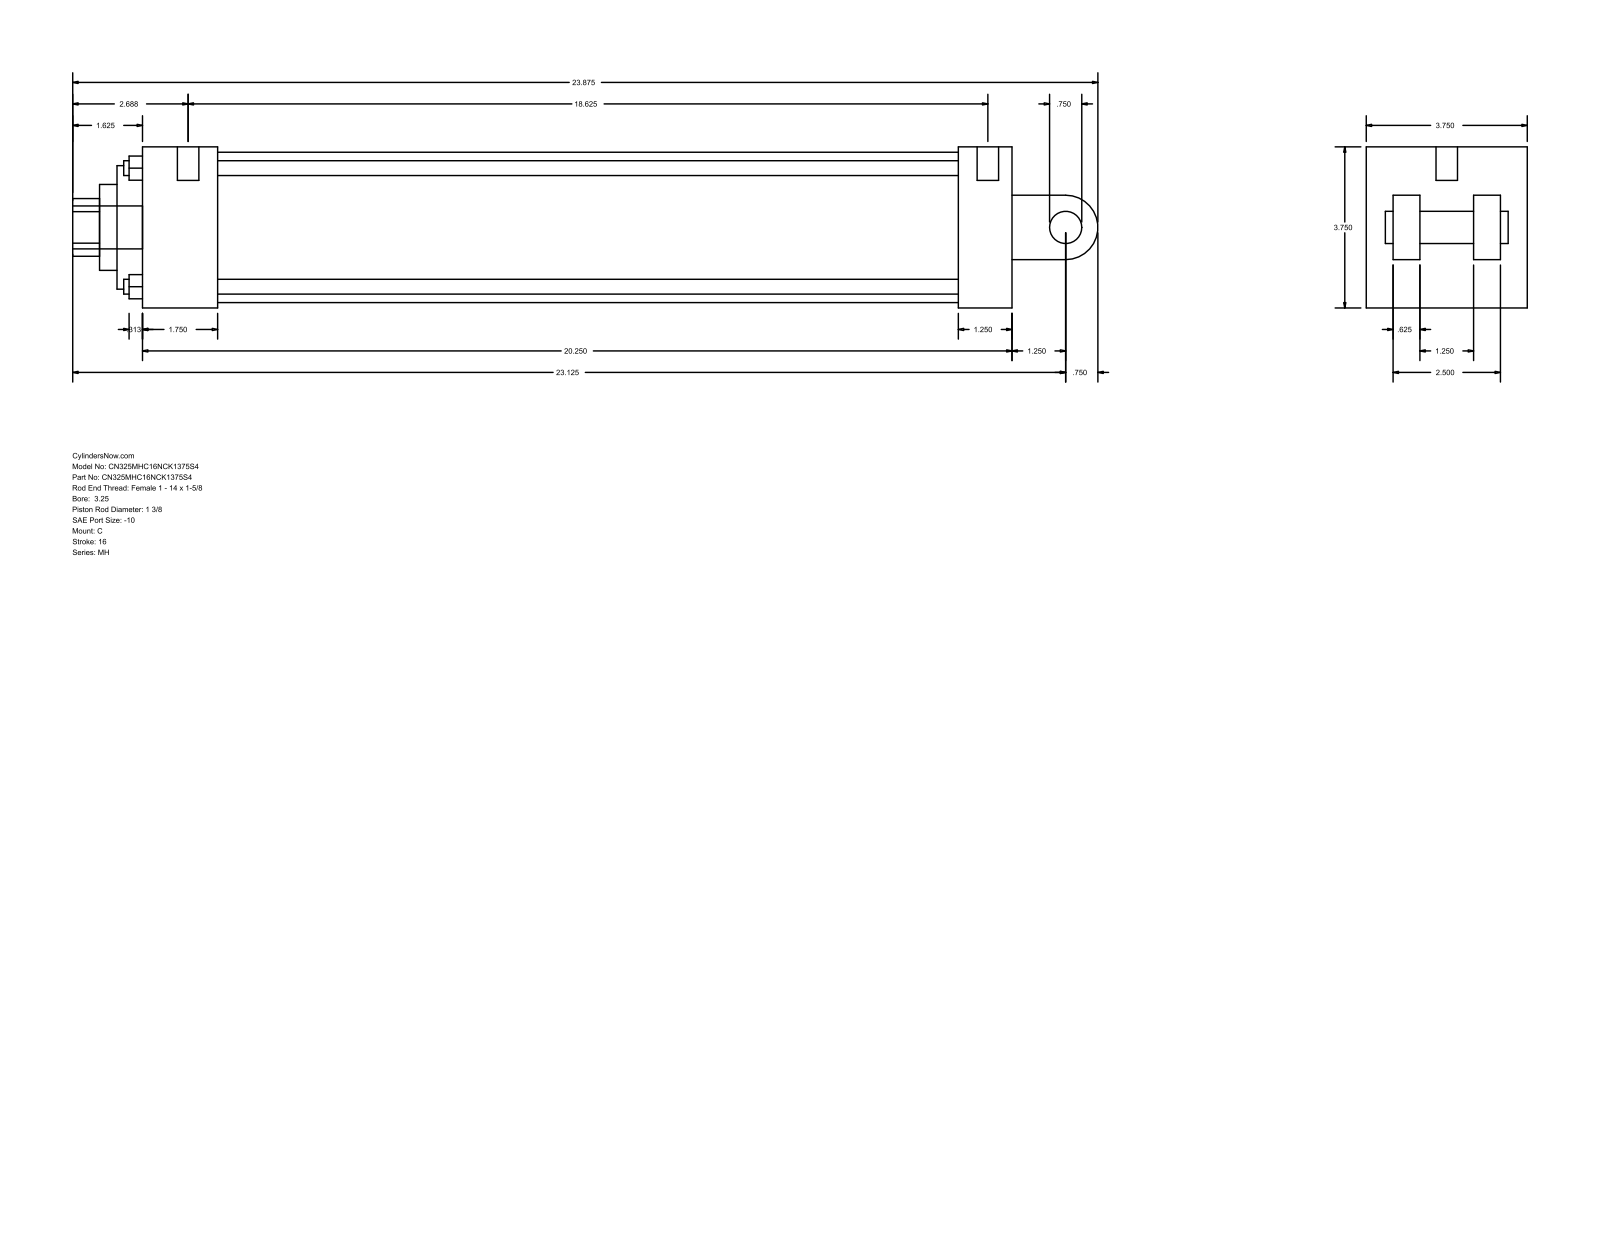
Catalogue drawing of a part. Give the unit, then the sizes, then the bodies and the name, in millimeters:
Units: millimetres
Overall size (bounding box): 606.42 × 95.25 × 95.25
Round holes (diameter × count): ⌀8.76 ×4, ⌀5.56 ×2, ⌀12.7 ×1, ⌀34.92 ×1, ⌀50.8 ×1, ⌀73.03 ×1, ⌀88.9 ×1
Round bosses / shafts (diameter × count): ⌀5.56 ×2, ⌀25.4 ×1, ⌀19.05 ×1, ⌀12.7 ×1
Partial cylindrical surfaces — rounded edges, fillets, slot ends (radius × count): R17.06 ×1, R19.05 ×1
Main face-to-face distances: 95.24, 15.87, 31.74, 514.35, 63.5, 79.37, 47.63, 44.45, 482.61, 438.16
Hole centre spacings: 49.57, 70.1, 99.14, 4.76
Bodies: 0 solids, 101 faces (71 planar, 30 cylindrical, 0 other)
Part name (STEP PRODUCT): MH_C__0325_1.375
STEP written by: GSSL Pune (CONFIG_CONTROL_DESIGN)
